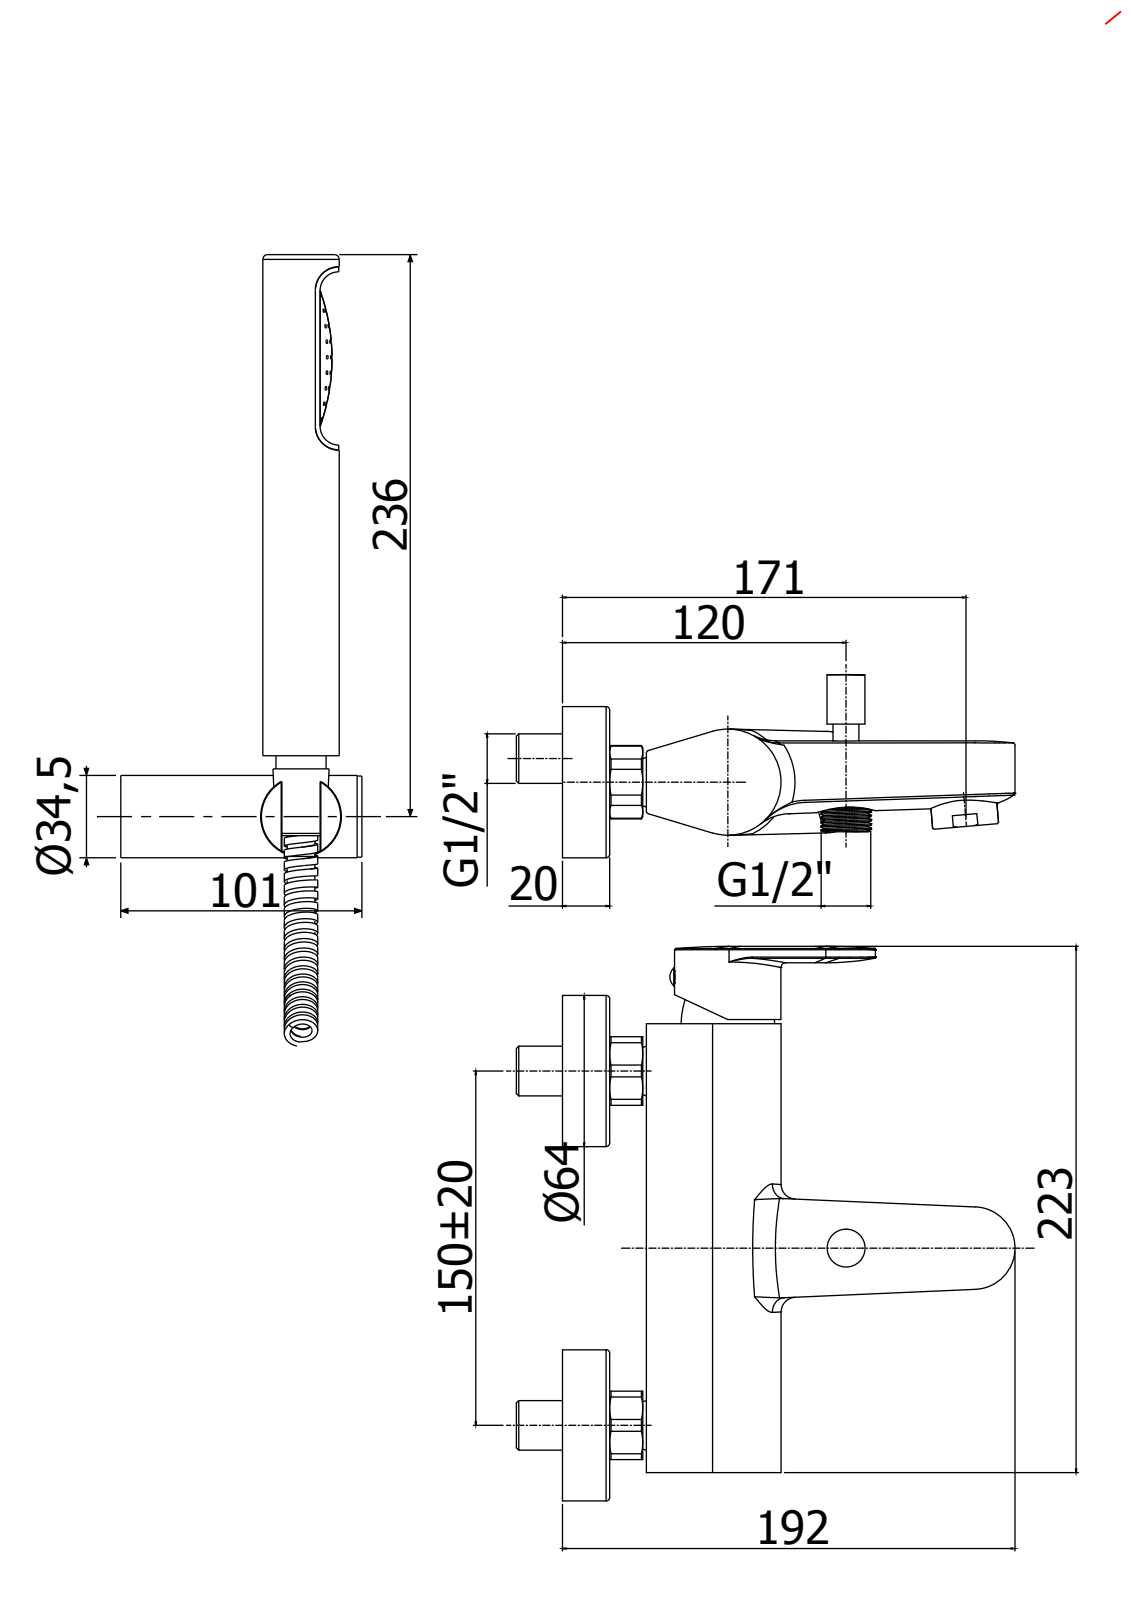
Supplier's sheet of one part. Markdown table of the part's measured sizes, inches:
| quantity | value |
| --- | --- |
| part name | CA023CR |
| STEP written by | CREO PARAMETRIC BY PTC INC, 2020044 (CONFIG_CONTROL_DESIGN) |
| units | inches |
| bodies | 6 solids, 1135 faces (298 planar, 429 cylindrical, 408 other) |
| overall size | 15.709 × 13.063 × 7.539 |
| volume | 30.4 in³ |
| surface area | 384.6 in² |
| round holes (diameter × count) | 0.059 × 45, 0.138 × 2, 0.413 × 2, 0.63 × 2, 0.65 × 2, 0.846 × 2, 1.122 × 2, 0.118 × 1, 0.177 × 1, 0.197 × 1, 0.307 × 1, 0.394 × 1 |
| round bosses / shafts (diameter × count) | 2.5 × 2, 0.827 × 2, 1.772 × 1, 1.358 × 1, 1.339 × 1, 1.331 × 1, 1.319 × 1, 1.26 × 1 |
| partial cylindrical surfaces (radius × count) | 0.039 × 91, 0.012 × 6, 0.079 × 4, 0.118 × 4, 0.197 × 4, 0.059 × 2, 0.307 × 2, 0.386 × 2 |
| main face-to-face distances | 0.138, 0.787, 1.358, 0.571, 0.118, 1.496, 0.709, 1.24, 1.949, 1.26 |
| hole center spacings | 0.311, 0.542, 0.256, 0.788, 0.512, 1.039, 0.177, 0.768 |
